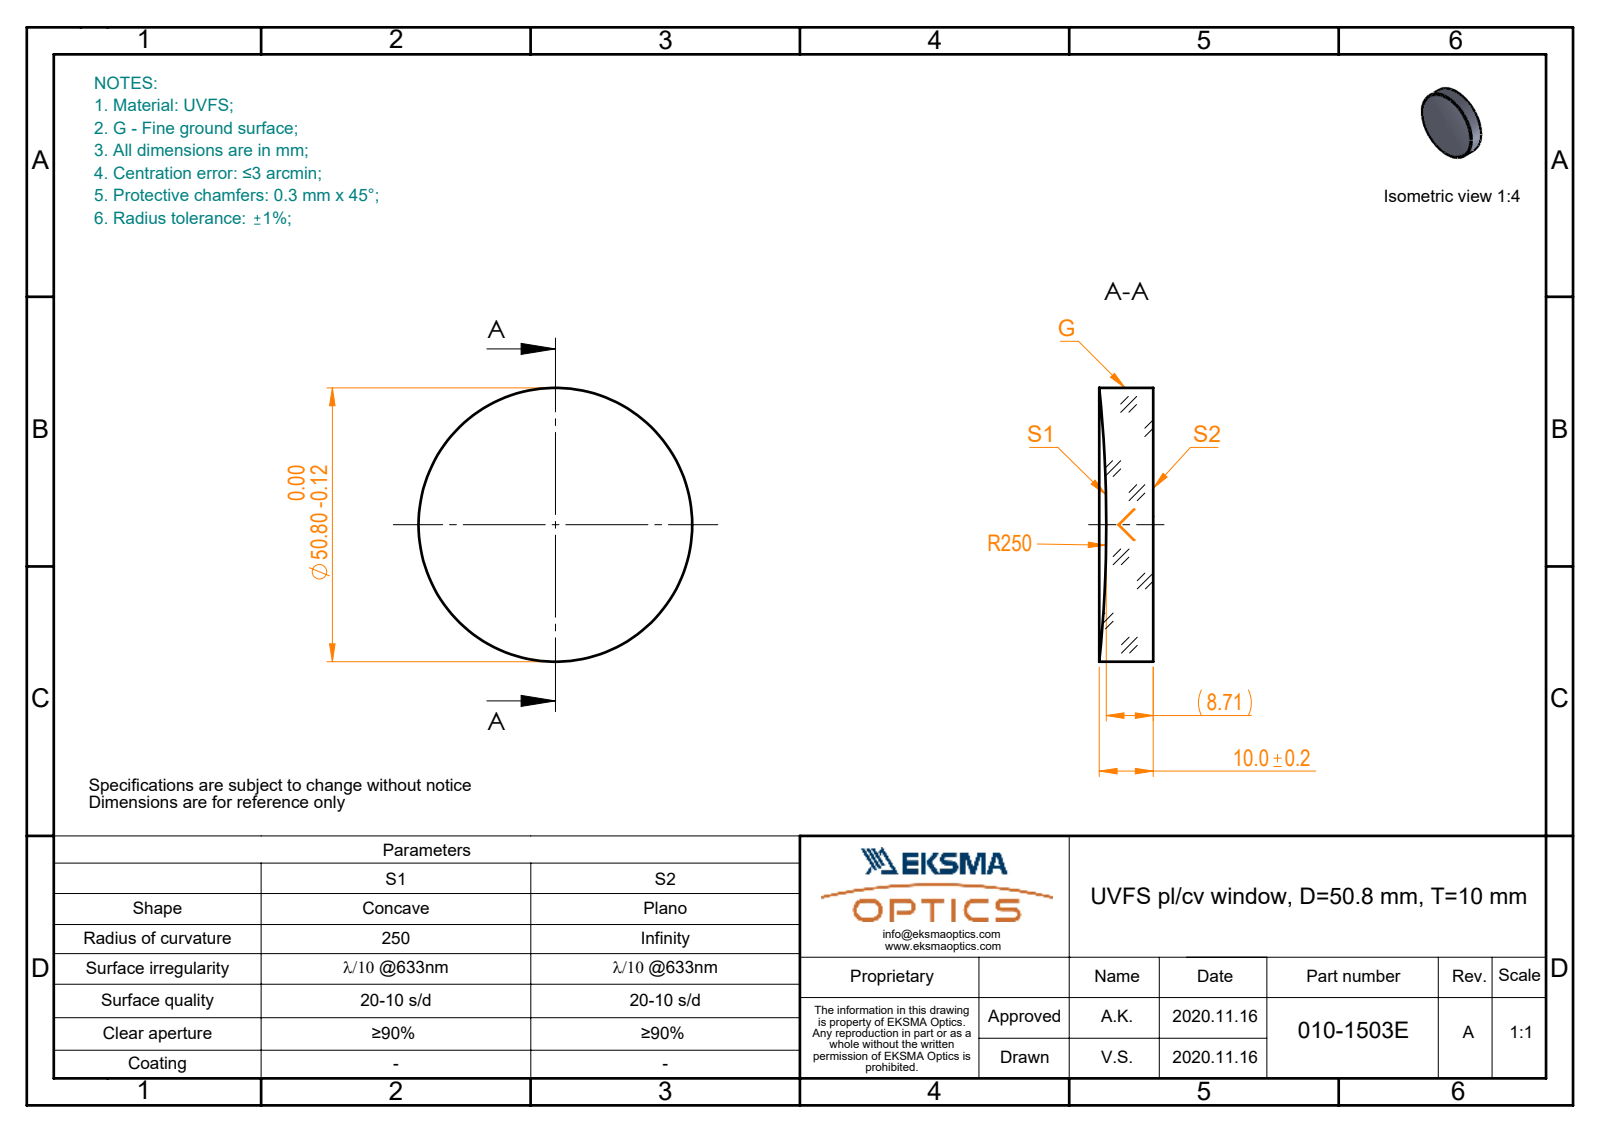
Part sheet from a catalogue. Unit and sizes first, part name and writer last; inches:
Units: inches
Overall size (bounding box): 2 × 2 × 0.394
Round bosses / shafts (diameter × count): ⌀2 ×1
Volume: 1.157 in³ · Surface area: 8.765 in²
Bodies: 1 solid, 5 faces (1 planar, 2 cylindrical, 2 other)
Part name (STEP PRODUCT): 010-1503E_UVFS_PCV_window
STEP written by: SolidWorks 2019 (CONFIG_CONTROL_DESIGN)
